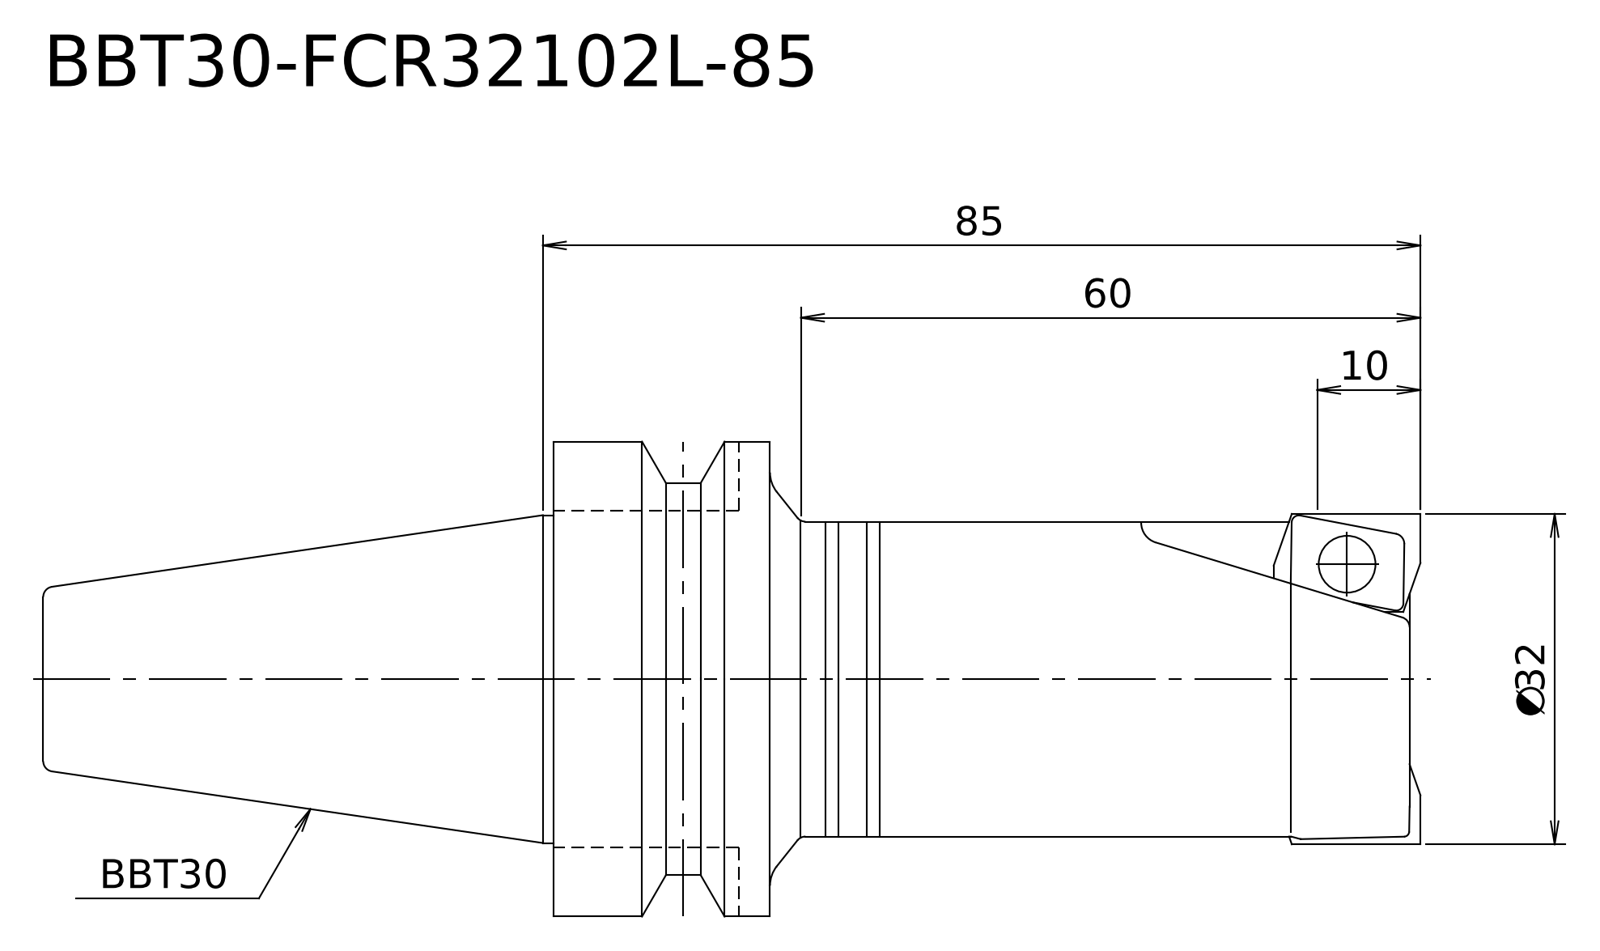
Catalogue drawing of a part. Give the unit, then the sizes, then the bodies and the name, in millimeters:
Units: millimetres
Overall size (bounding box): 133.4 × 46 × 46
Round bosses / shafts (diameter × count): ⌀46 ×1, ⌀38 ×1, ⌀32 ×1, ⌀31.75 ×1, ⌀30.5 ×1
Main face-to-face distances: 84, 63, 21, 133.4, 70.4, 49.4
Volume: 103 929 mm³ · Surface area: 16 151 mm²
Bodies: 1 solid, 17 faces (4 planar, 6 cylindrical, 7 other)
STEP written by: Kubotek KeyCreator V8.5.1 (14335) (CONFIG_CONTROL_DESIGN)
